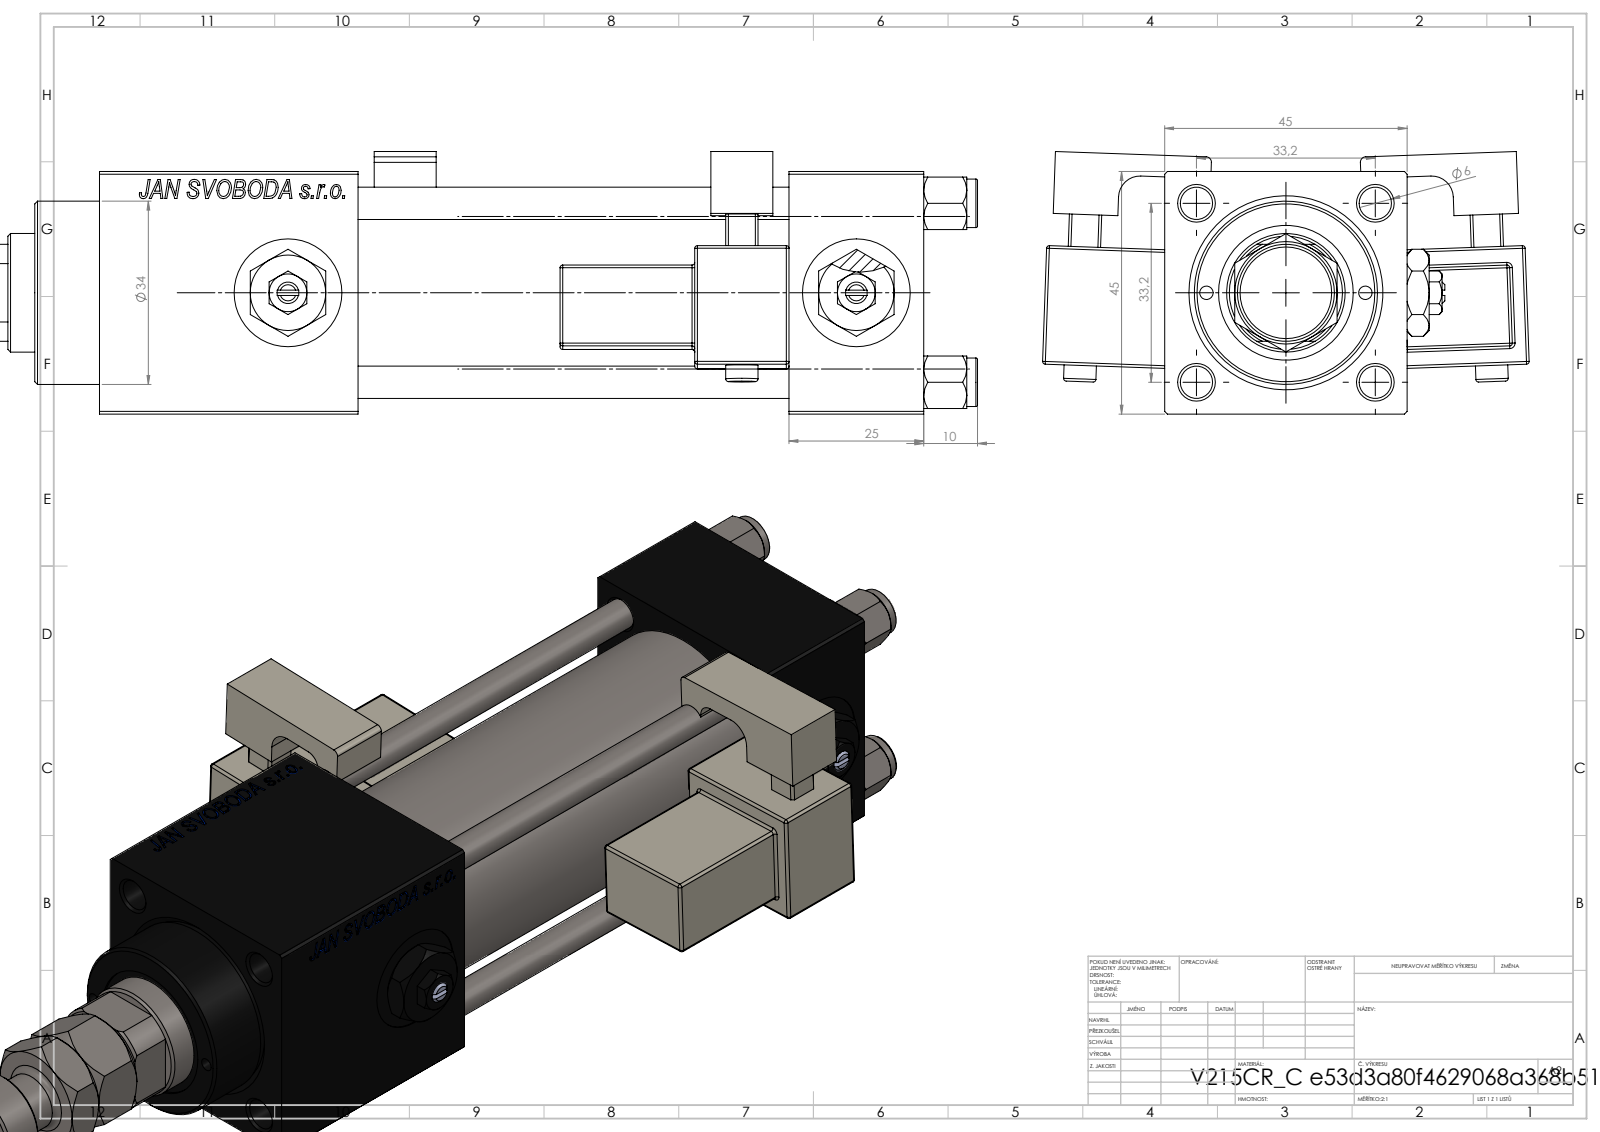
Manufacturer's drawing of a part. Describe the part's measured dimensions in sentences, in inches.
The part is named "V215CR_C_TYCINKA; V215CR_C_Body; V215CR_MSU; Zatka_pro_OIL_PORT (+4 more)". Its 3-D file was written by "SolidWorks 2019 (CONFIG_CONTROL_DESIGN)". It is 16 solids with 1464 faces: 652 planar, 166 cylindrical and 646 other. Overall it measures 8.701 by 3.556 by 1.918 inches. Its volume is 17.18 cubic inches and its surface area 153.5 square inches. Round holes: 4 of diameter 0.236, 2 of diameter 0.098, 2 of diameter 0.276, 2 of diameter 0.518, 2 of diameter 0.787, 1 of diameter 0.413, 1 of diameter 0.866, 1 of diameter 0.945, 1 of diameter 0.984, 1 of diameter 1.26, 1 of diameter 1.299. Round bosses or shafts: 4 of diameter 0.354, 2 of diameter 0.236, 1 of diameter 1.496, 1 of diameter 1.339, 1 of diameter 0.709, 1 of diameter 0.433. Partial cylindrical surfaces (rounded edges, fillets, slot ends): 48 of radius 0.02, 2 of radius 0.039, 2 of radius 0.098, 2 of radius 0.157, 1 of radius 0.413. The main face-to-face distances are 1.772, 0.984, 0.118, 4.134, 3.15, 6.024, 0.905, 2.461, 1.89, 5.039. The hole center spacings are 0.657, 0.924, 1.307, 1.396, 0.581, 1.848, 1.161, 4.154.
